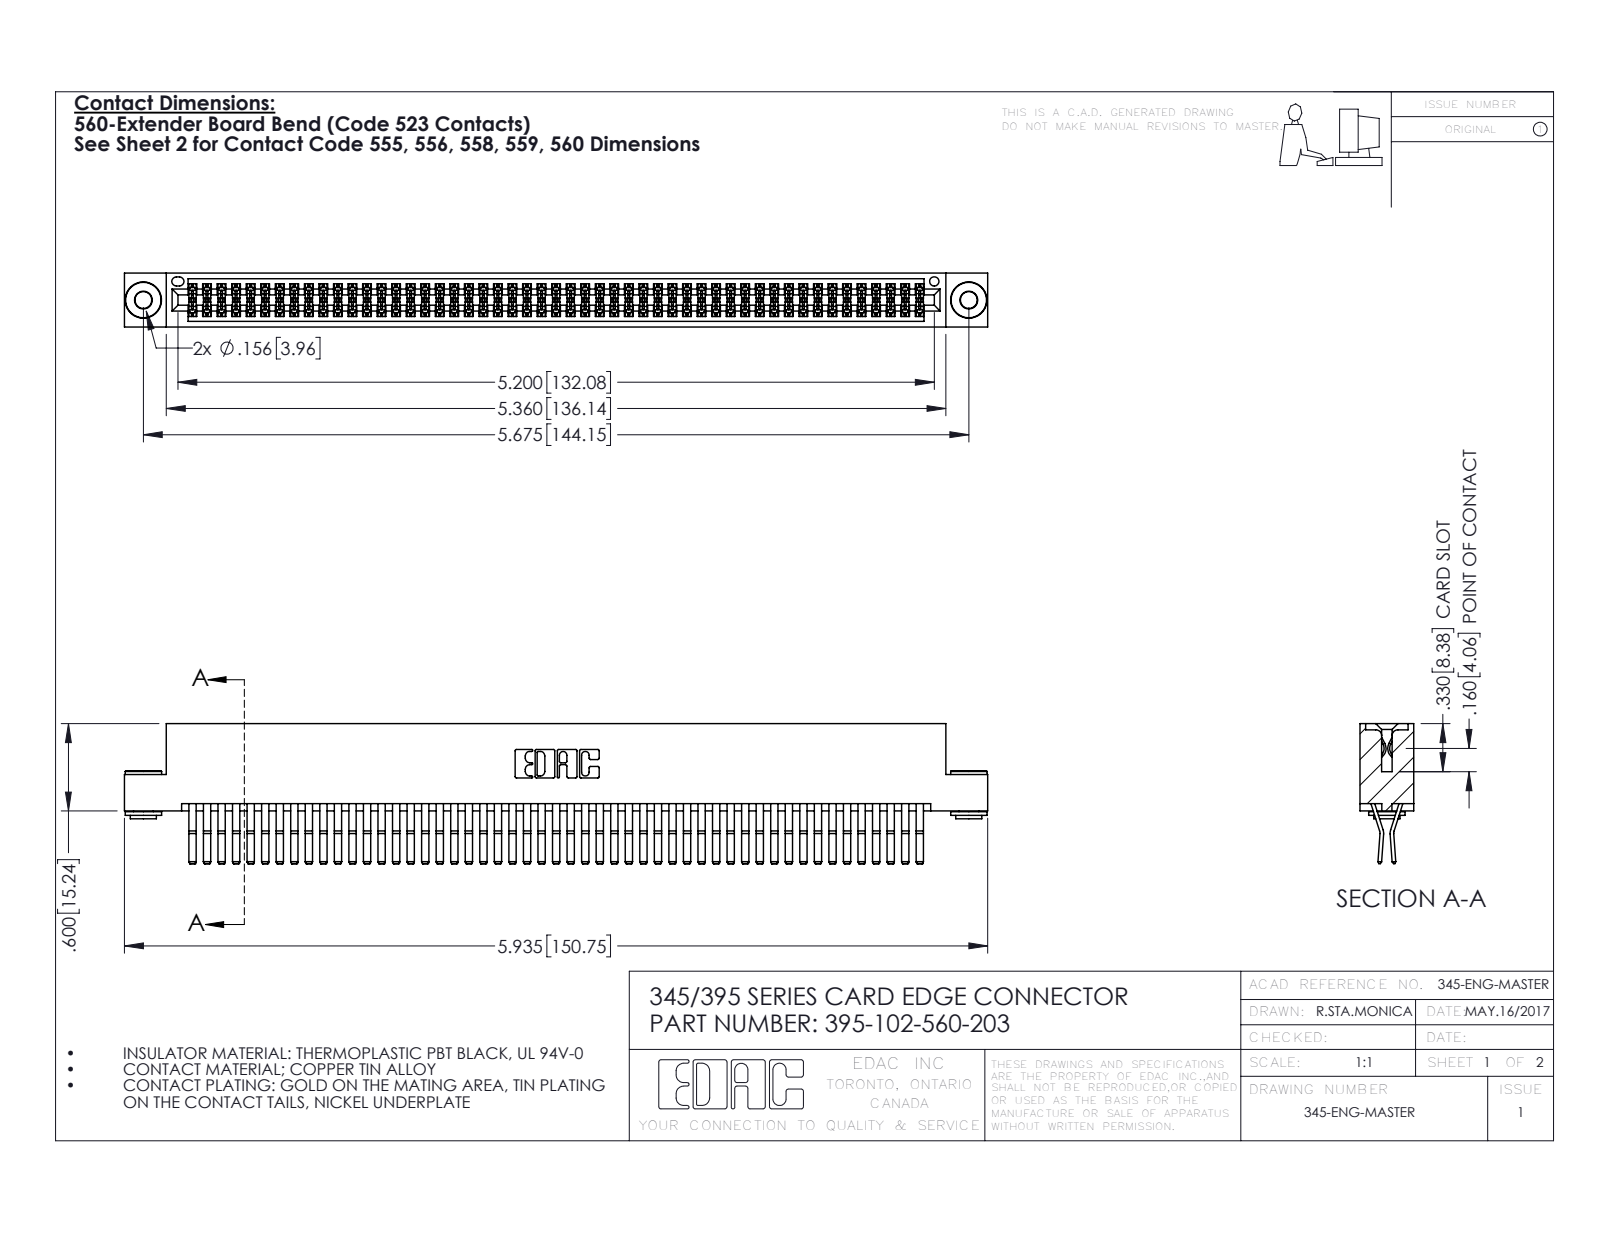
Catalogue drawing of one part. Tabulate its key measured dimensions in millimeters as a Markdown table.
| quantity | value |
| --- | --- |
| part name | 345-292-001_560 Tail; 345-250-002_345-250-002-102; 345 Part_Flush Mounting Lugs - 0.156 Dia-TH; 395-102-560-203 |
| STEP written by | SolidWorks 2016 (CONFIG_CONTROL_DESIGN) |
| units | millimeters |
| bodies | 105 solids, 5468 faces (3456 planar, 2004 cylindrical, 8 other) |
| overall size | 150.7 × 24.4 × 9.4 |
| volume | 15 400 mm³ |
| surface area | 24 880 mm² |
| round holes (diameter × count) | 2.9 × 2, 4 × 2, 1.6 × 1 |
| round bosses / shafts (diameter × count) | 6.4 × 2, 4.6 × 2, 3.5 × 2 |
| partial cylindrical surfaces (radius × count) | 0.2 × 154, 0.3 × 22, 0.2 × 6, 0.8 × 6, 0.7 × 3, 0.3 × 2, 0.4 × 2, 0.5 × 2 |
| main face-to-face distances | 0.6, 1.8, 7.6, 5.1, 9.4, 2.5, 6.9, 5.7, 4.4, 3.8 |
| hole center spacings | 6.9, 138.2, 144.1 |
